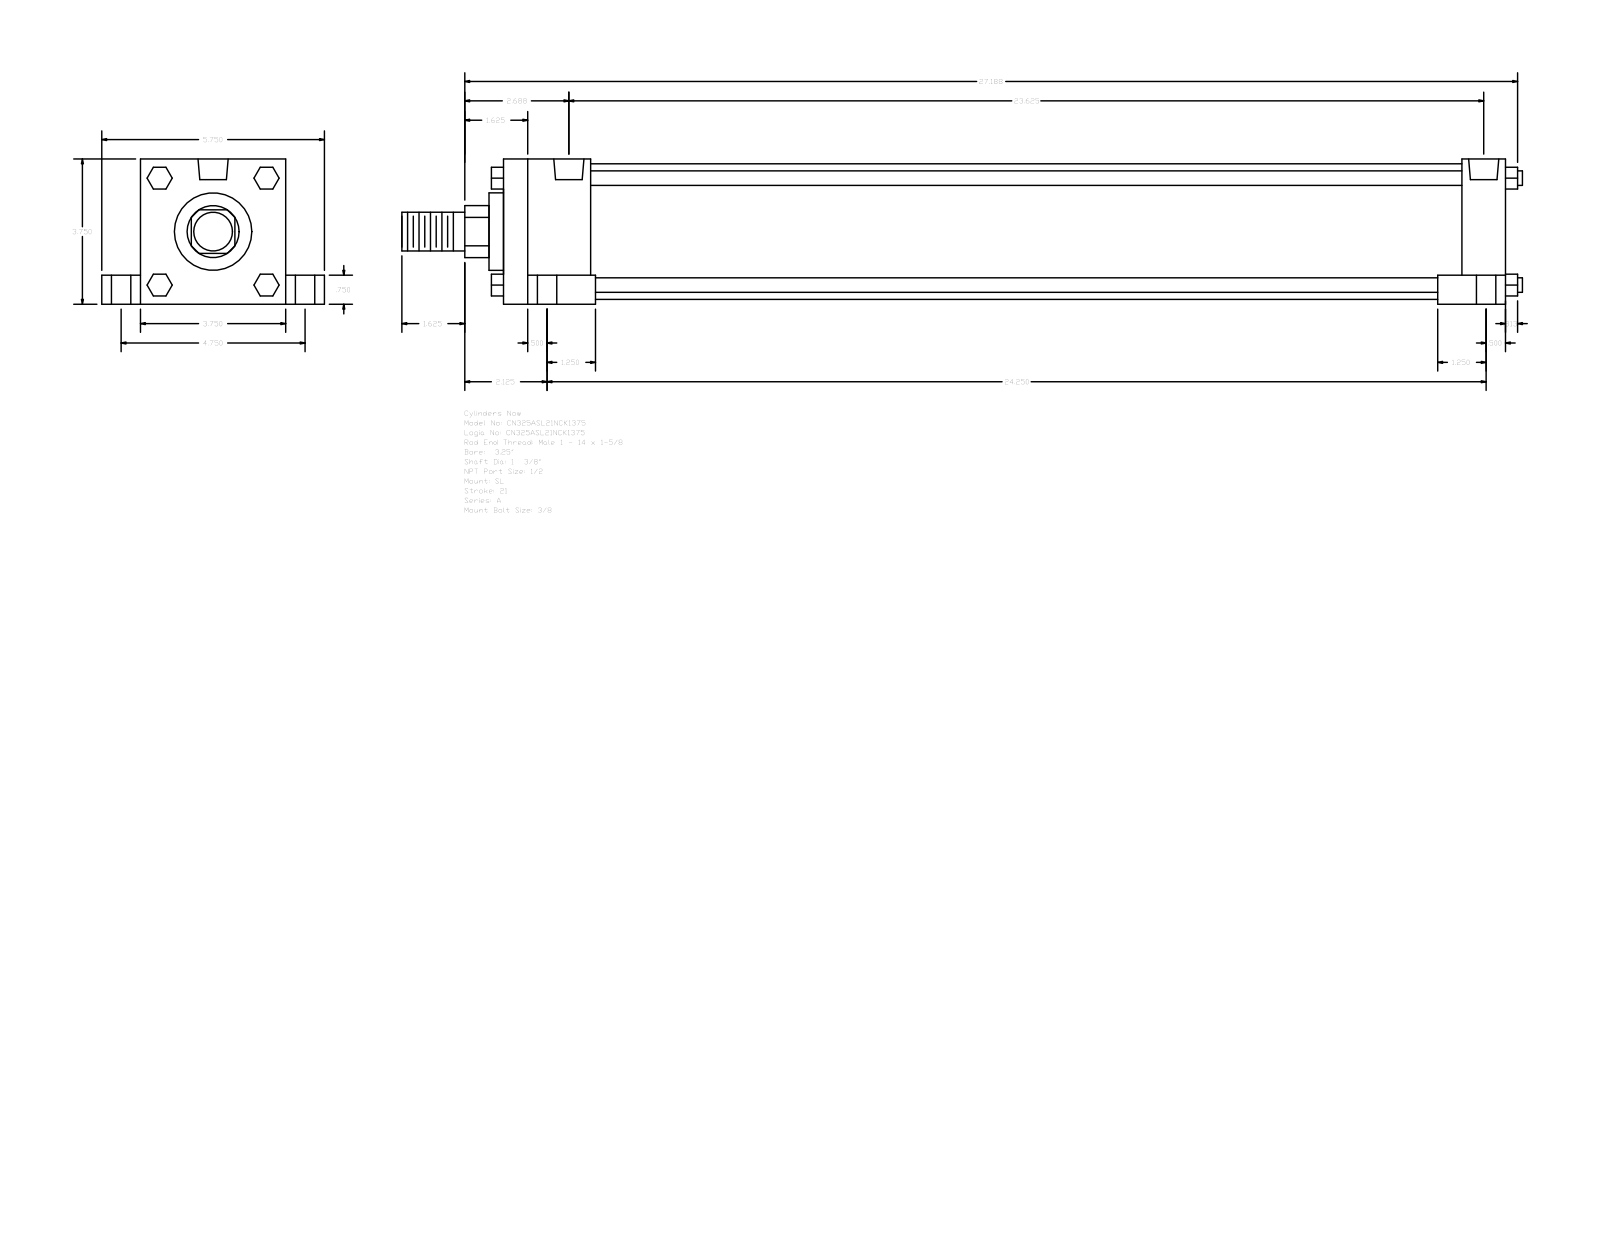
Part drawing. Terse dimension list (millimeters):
name: A_SL__0325_1.375
written by: GSSL Pune (CONFIG_CONTROL_DESIGN)
unit: mm
bodies: 0 solids, 150 faces (114 planar, 36 cylindrical, 0 other)
size: 735.01 × 146.05 × 95.25
holes: 4× ⌀8.73, 4× ⌀12.7, 4× ⌀19.05, 2× ⌀19.77
bosses: 4× ⌀9.53, 1× ⌀88.9, 1× ⌀50.8, 1× ⌀34.92, 1× ⌀25.4
rounds: 1× R17.06
face distances: 95.24, 657.22, 25.41, 120.65, 19.05, 76.19, 57.15, 28.57, 628.65, 571.5
hole spacings: 3.18, 60.35, 60.52, 62, 62.81, 120.66, 593.72, 596.9
